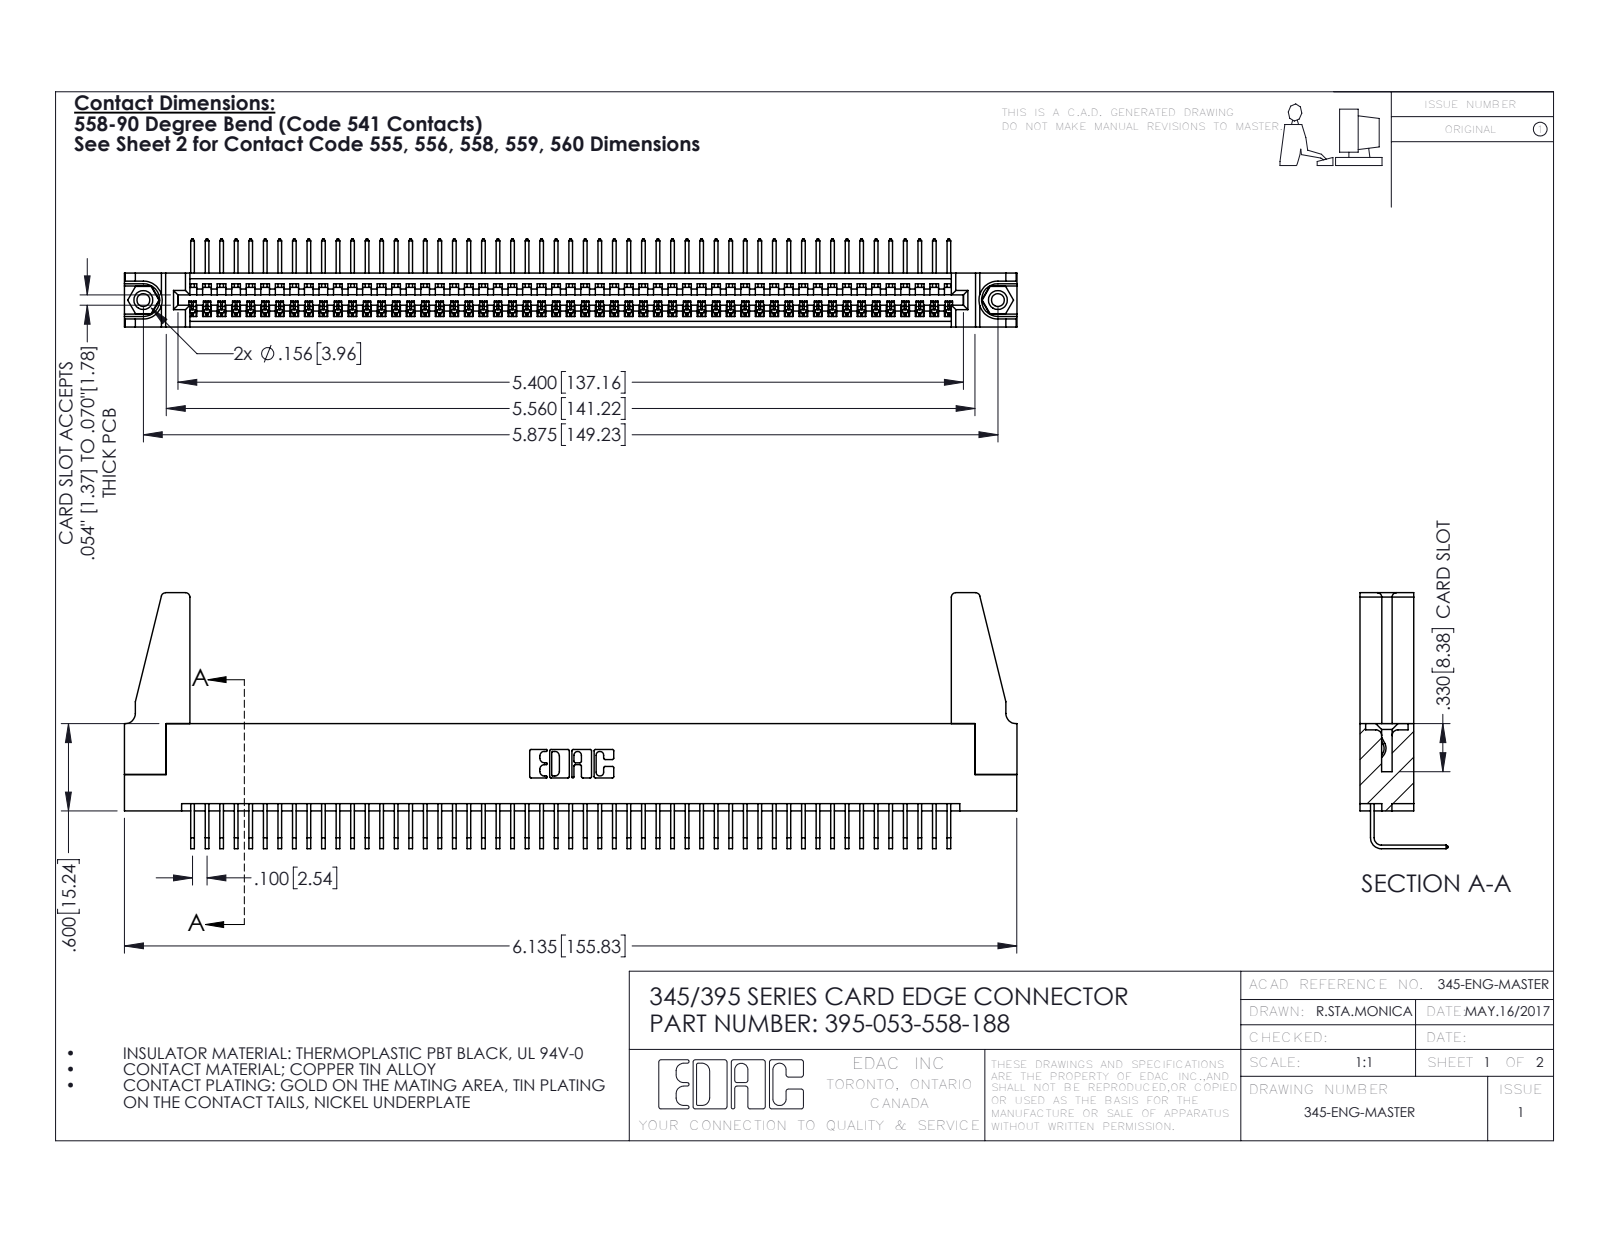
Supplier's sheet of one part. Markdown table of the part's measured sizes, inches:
| quantity | value |
| --- | --- |
| part name | 345-250-001_345-250-001-102; 345-220-078_345-220-088; 395-053-558-188; 345-292-001_558 Tail - 2 (+1 more) |
| STEP written by | SolidWorks 2016 (CONFIG_CONTROL_DESIGN) |
| units | inches |
| bodies | 58 solids, 3430 faces (2378 planar, 1036 cylindrical, 16 other) |
| overall size | 6.136 × 1.759 × 0.605 |
| volume | 1.118 in³ |
| surface area | 37.73 in² |
| round holes (diameter × count) | 0.089 × 2, 0.125 × 2, 0.156 × 2, 0.064 × 1 |
| round bosses / shafts (diameter × count) | 0.155 × 2 |
| partial cylindrical surfaces (radius × count) | 0.006 × 106, 0.01 × 22, 0.03 × 8, 0.007 × 6, 0.031 × 6, 0.026 × 3, 0.031 × 2, 0.04 × 2 |
| main face-to-face distances | 0.072, 0.298, 0.37, 0.2, 0.098, 0.272, 0.025, 0.225, 0.149, 0.072 |
| hole center spacings | 0.27, 5.639, 5.875 |
